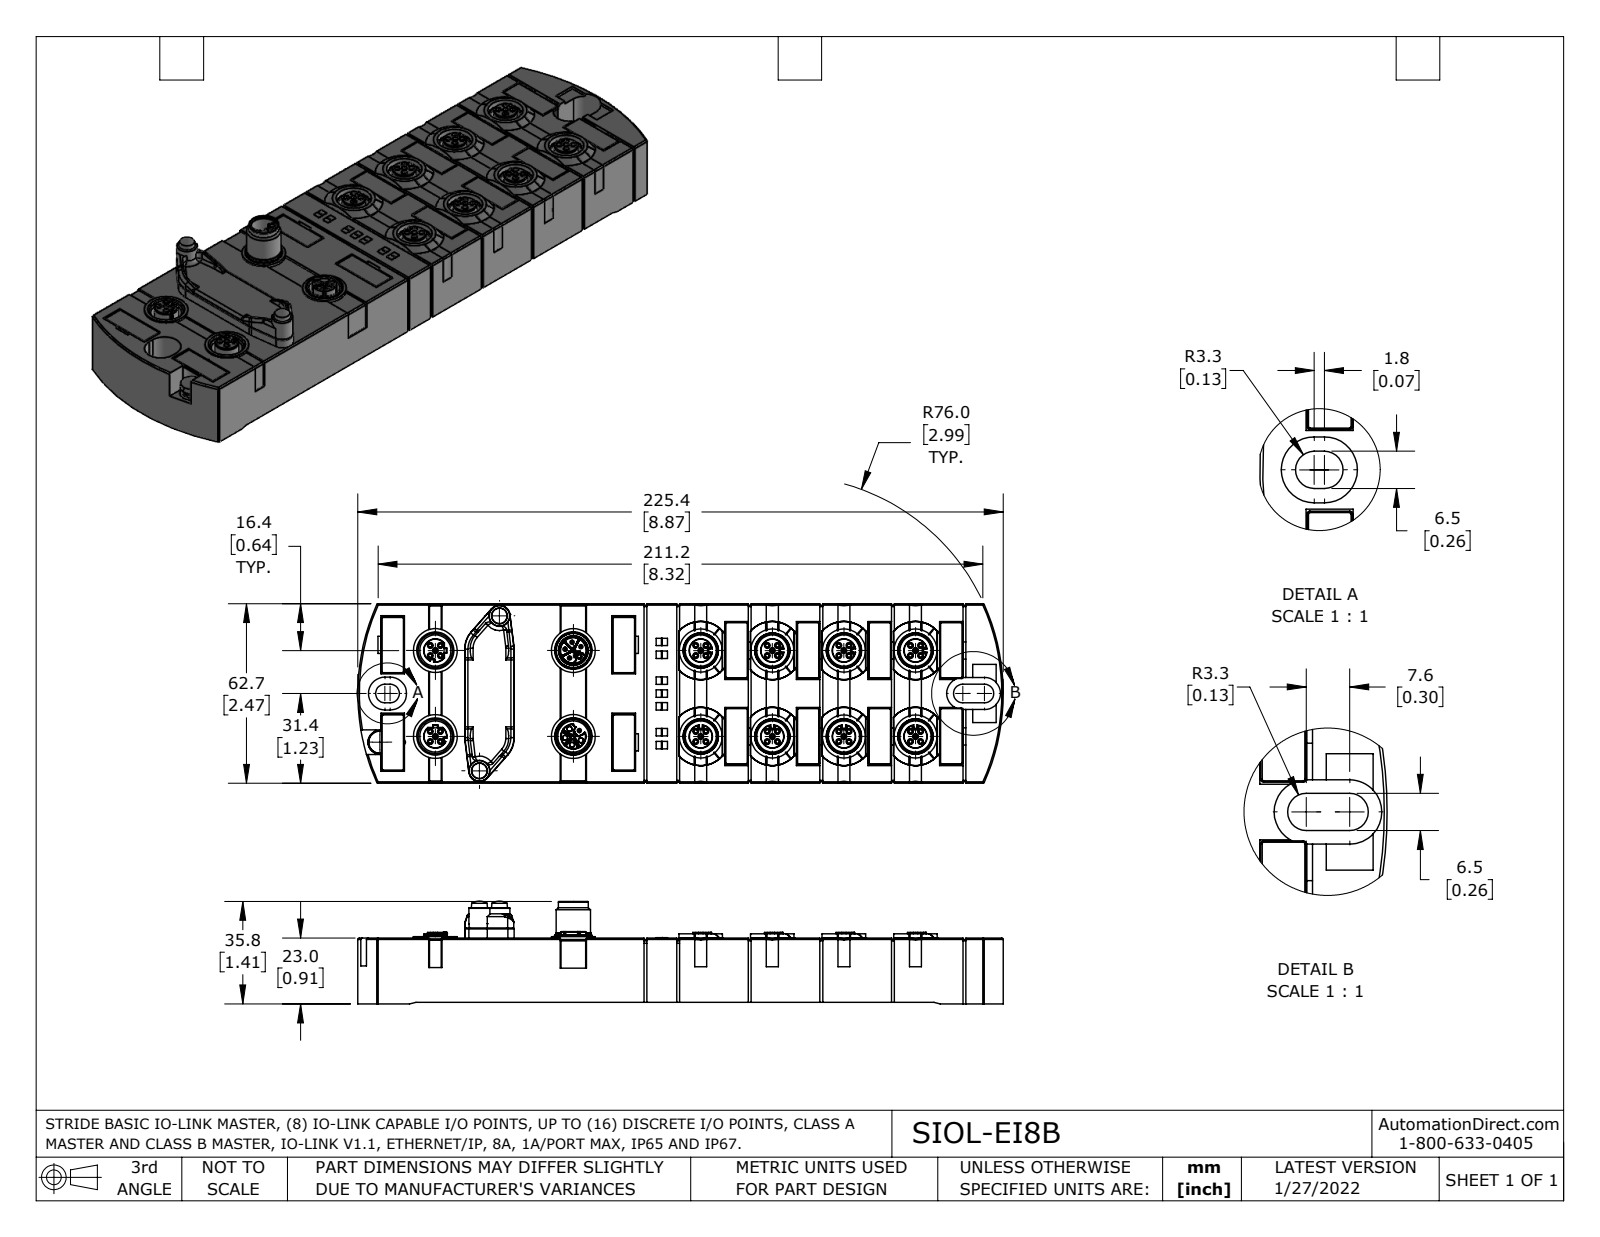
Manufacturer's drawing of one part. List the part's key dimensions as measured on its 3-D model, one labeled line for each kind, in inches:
Part name (STEP PRODUCT): SIOL-EI8B
STEP written by: SolidWorks 2021 (AUTOMOTIVE_DESIGN)
Units: inches
Bodies: 2 solids, 2019 faces (734 planar, 668 cylindrical, 617 other)
Overall size (bounding box): 8.874 × 2.469 × 1.413
Volume: 18.87 in³ · Surface area: 85.23 in²
Round holes (diameter × count): ⌀0.047 ×50, ⌀0.43 ×9, ⌀0.065 ×4, ⌀0.43 ×2, ⌀0.512 ×2, ⌀0.128 ×1, ⌀0.161 ×1, ⌀0.35 ×1
Round bosses / shafts (diameter × count): ⌀0.079 ×50, ⌀0.323 ×10, ⌀0.059 ×5, ⌀0.602 ×4, ⌀0.516 ×2, ⌀0.289 ×2, ⌀0.484 ×1, ⌀0.472 ×1
Partial cylindrical surfaces — rounded edges, fillets, slot ends (radius × count): R0.02 ×64, R0.039 ×21, R0.01 ×20, R0.008 ×15, R0.006 ×14, R0.004 ×13, R0.394 ×12, R0.012 ×10
Main face-to-face distances: 0.882, 2.469, 0.024, 0.906, 0.904, 0.88, 0.02, 0.217, 0.059, 0.199
Hole centre spacings: 0.139, 0.984, 1.537, 0.098, 0.994, 1.181, 0.196, 1.189
